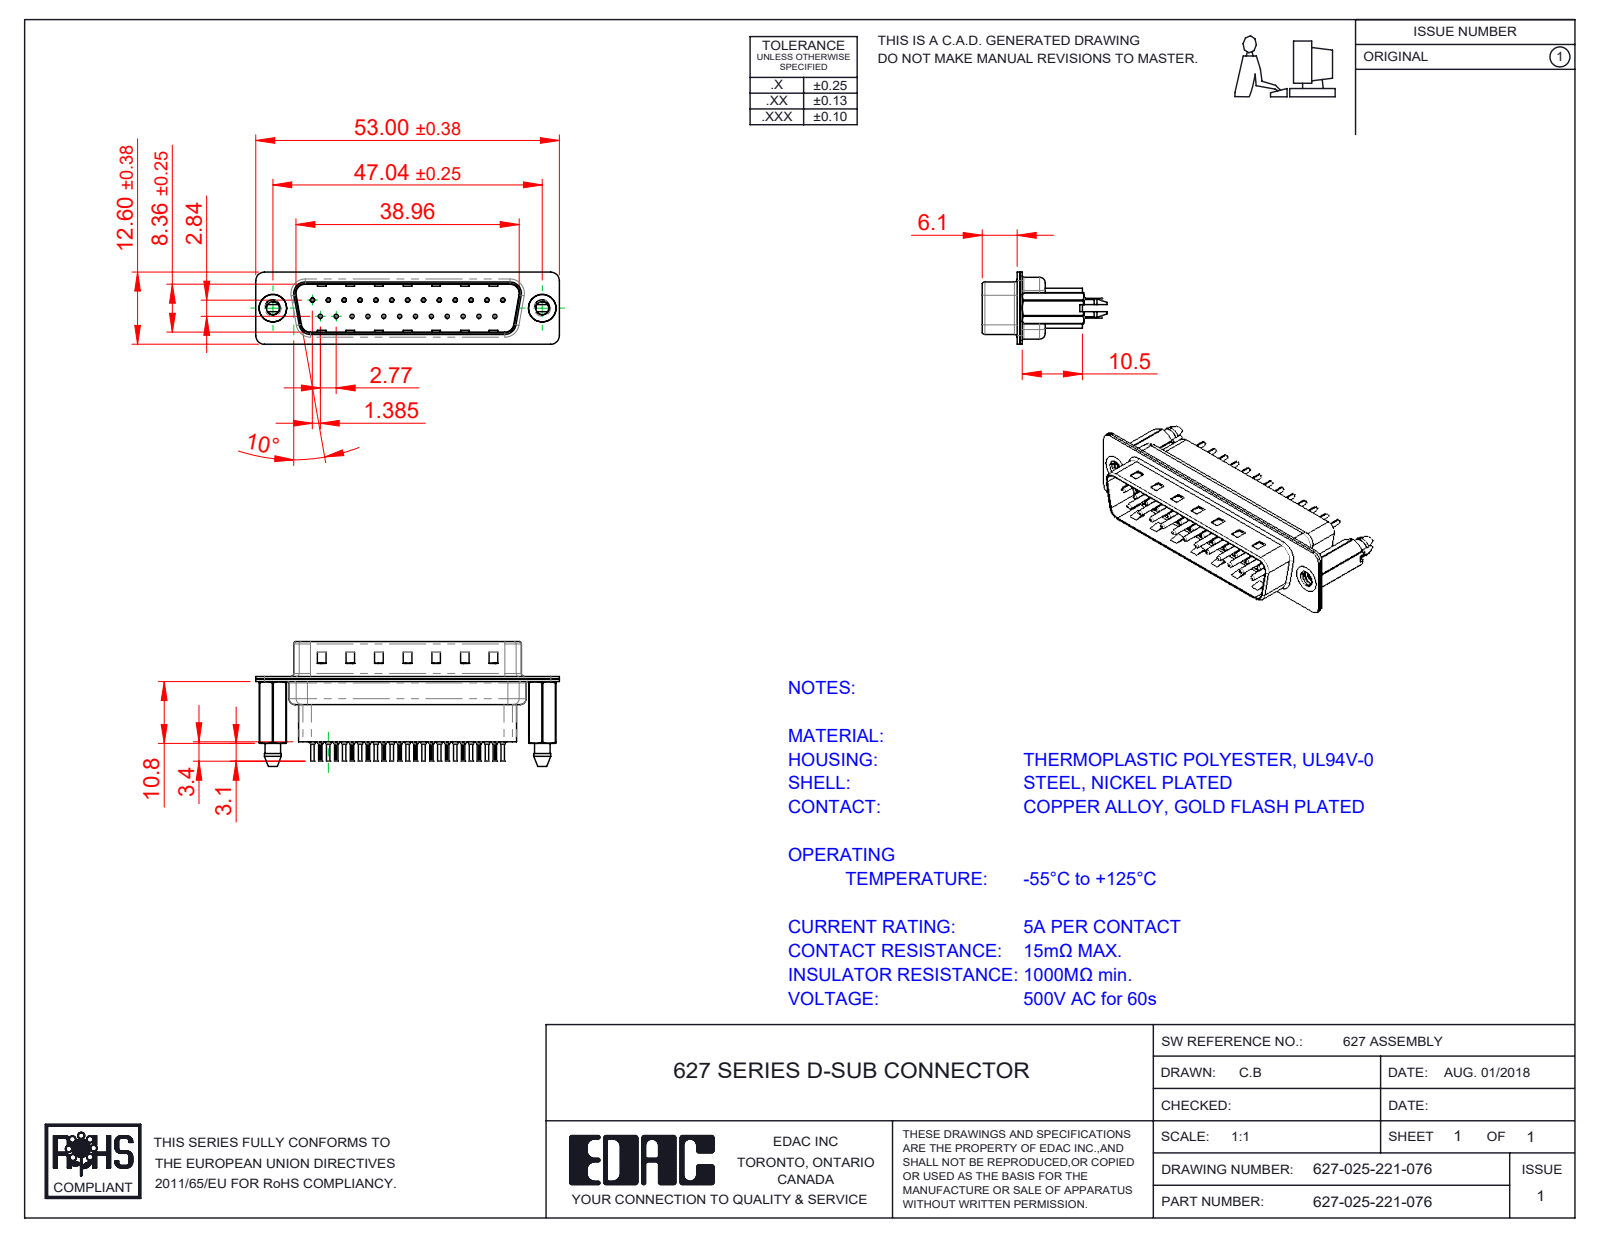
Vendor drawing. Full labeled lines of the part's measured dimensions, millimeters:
Part name (STEP PRODUCT): 627 Contact Row 1_21H; 627 Housing_25 HP; 627 Shell Rear_25 Contacts; 627 Contact Row 2_21H (+3 more)
STEP written by: SolidWorks 2020 (CONFIG_CONTROL_DESIGN)
Units: millimetres
Bodies: 30 solids, 2940 faces (803 planar, 1130 cylindrical, 1007 other)
Overall size (bounding box): 53 × 21.7 × 12.6
Volume: 4 049 mm³ · Surface area: 10 359 mm²
Round holes (diameter × count): ⌀0.2 ×25, ⌀0.35 ×25, ⌀1.1 ×25, ⌀1.6 ×25, ⌀2.26 ×2, ⌀4 ×2, ⌀4.8 ×2
Round bosses / shafts (diameter × count): ⌀2 ×25, ⌀1.5 ×25, ⌀0.75 ×25, ⌀0.6 ×25, ⌀4.9 ×2
Partial cylindrical surfaces — rounded edges, fillets, slot ends (radius × count): R0.1 ×50, R1.5 ×18, R2 ×12, R1.6 ×10, R0.5 ×8, R0.25 ×4, R0.6 ×4, R0.65 ×4
Main face-to-face distances: 0.4, 0.45, 0.82, 9.58, 0.68, 7.68, 1.5, 0.9, 1.08, 8.08
Hole centre spacings: 3.16, 8.31, 2.77, 5.54, 11.08, 16.62, 5.03, 5.04
